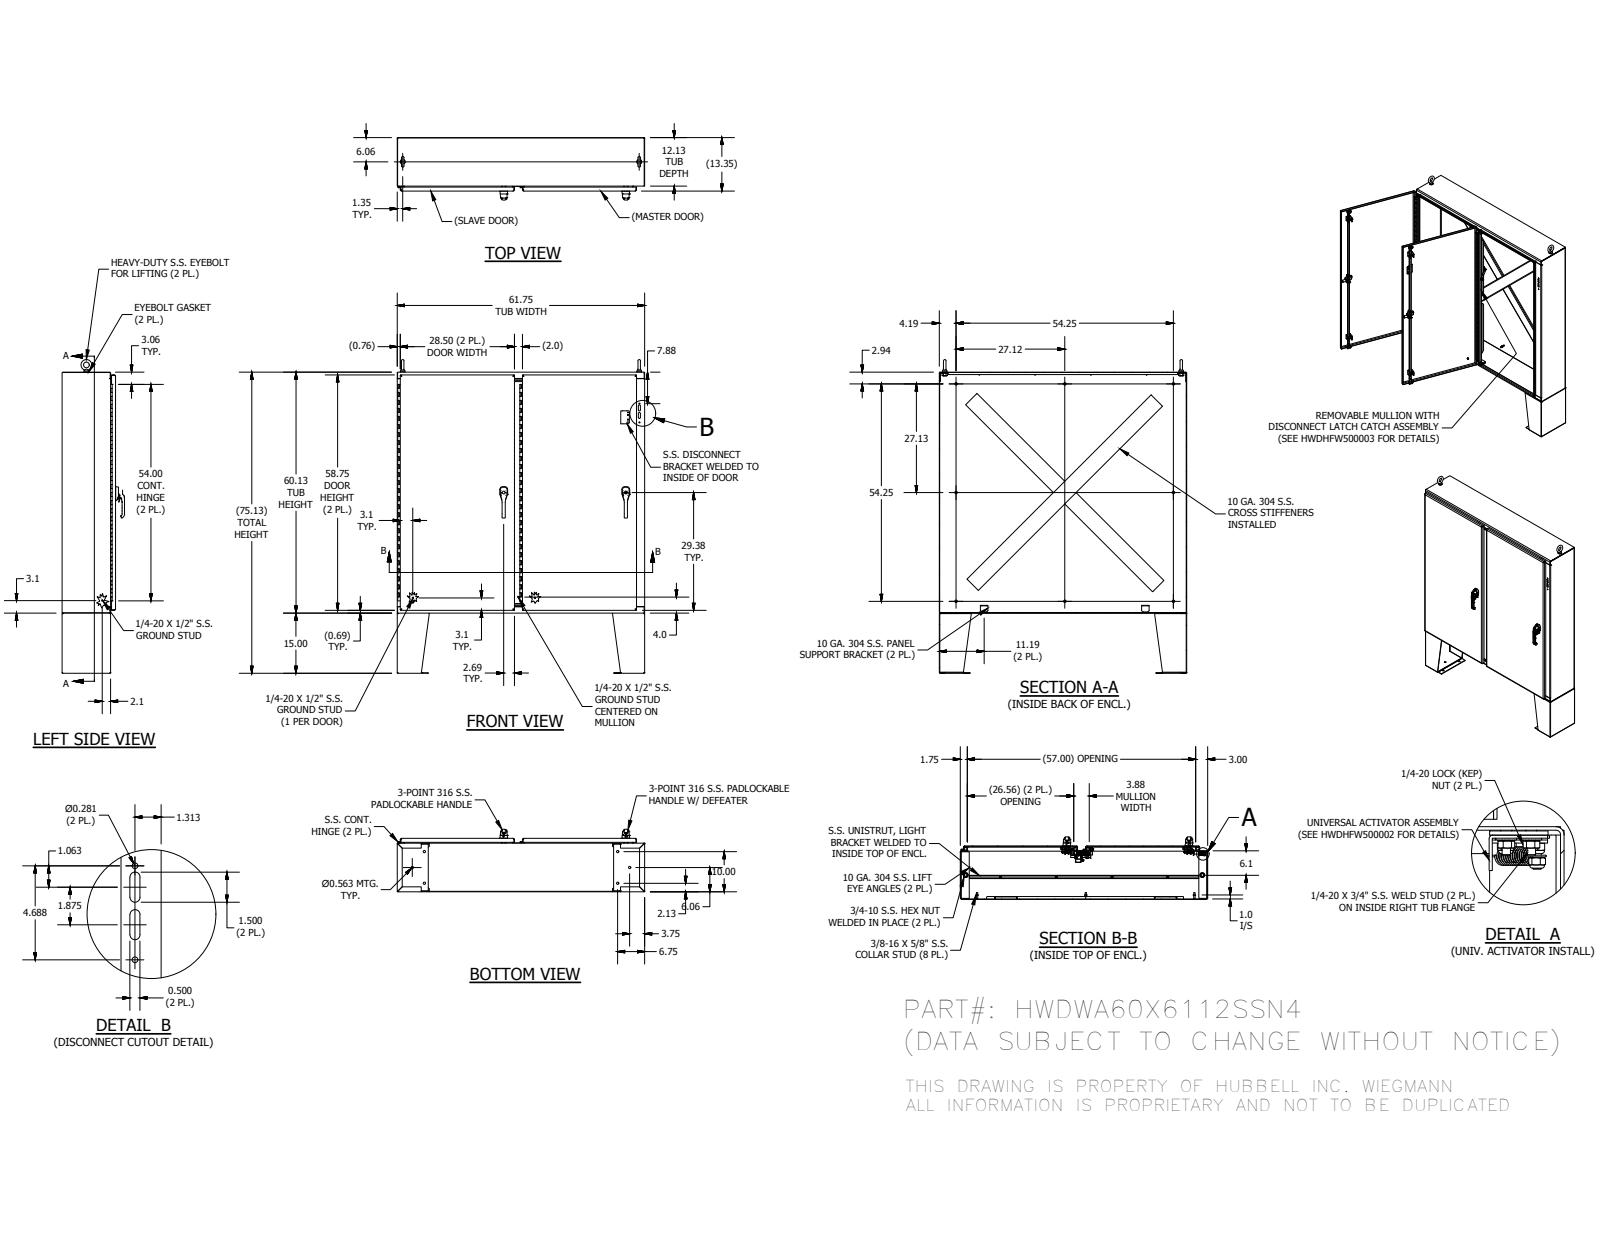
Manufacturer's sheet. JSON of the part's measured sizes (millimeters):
{"part_name": "WA60X6112SSN4BLR; WAX6112SSN4TOP; WAX6112SSN4BTM; HFW332010S (+8 more)", "step_written_by": "Autodesk Inventor 2016 (AUTOMOTIVE_DESIGN)", "units": "millimeters", "bodies": {"solids": 220, "faces": 9034, "planar": 4178, "cylindrical": 3056, "other": 1800}, "overall_size": [1987.49, 1568.45, 396.15], "volume_mm3": 24610000, "surface_area_mm2": 18620000, "round_holes": [[6.35, 18], [9.52, 18], [14.29, 18], [4.76, 9], [4.83, 8], [4.98, 8], [6.65, 8], [7.33, 8], [8.51, 8], [9.65, 8], [3.96, 6], [5.4, 6]], "round_bosses_or_shafts": [[6.35, 19], [8.38, 18], [15.88, 13], [8.56, 12], [9.52, 11], [14.29, 9], [7.11, 8], [25.4, 6]], "partial_cylinders_radius": [[0.5, 359], [0.3, 221], [0.51, 192], [3.17, 55], [0.47, 42], [1.27, 28], [2, 28], [6.35, 23]], "face_to_face_distances": [2.64, 336.39, 333.75, 339.03, 1524.54, 1565.8, 305.33, 31.06, 3.17, 302.69], "hole_center_spacings": [9.65, 19.31, 30.36, 37.06, 98.31, 124.21, 126.05, 127]}
